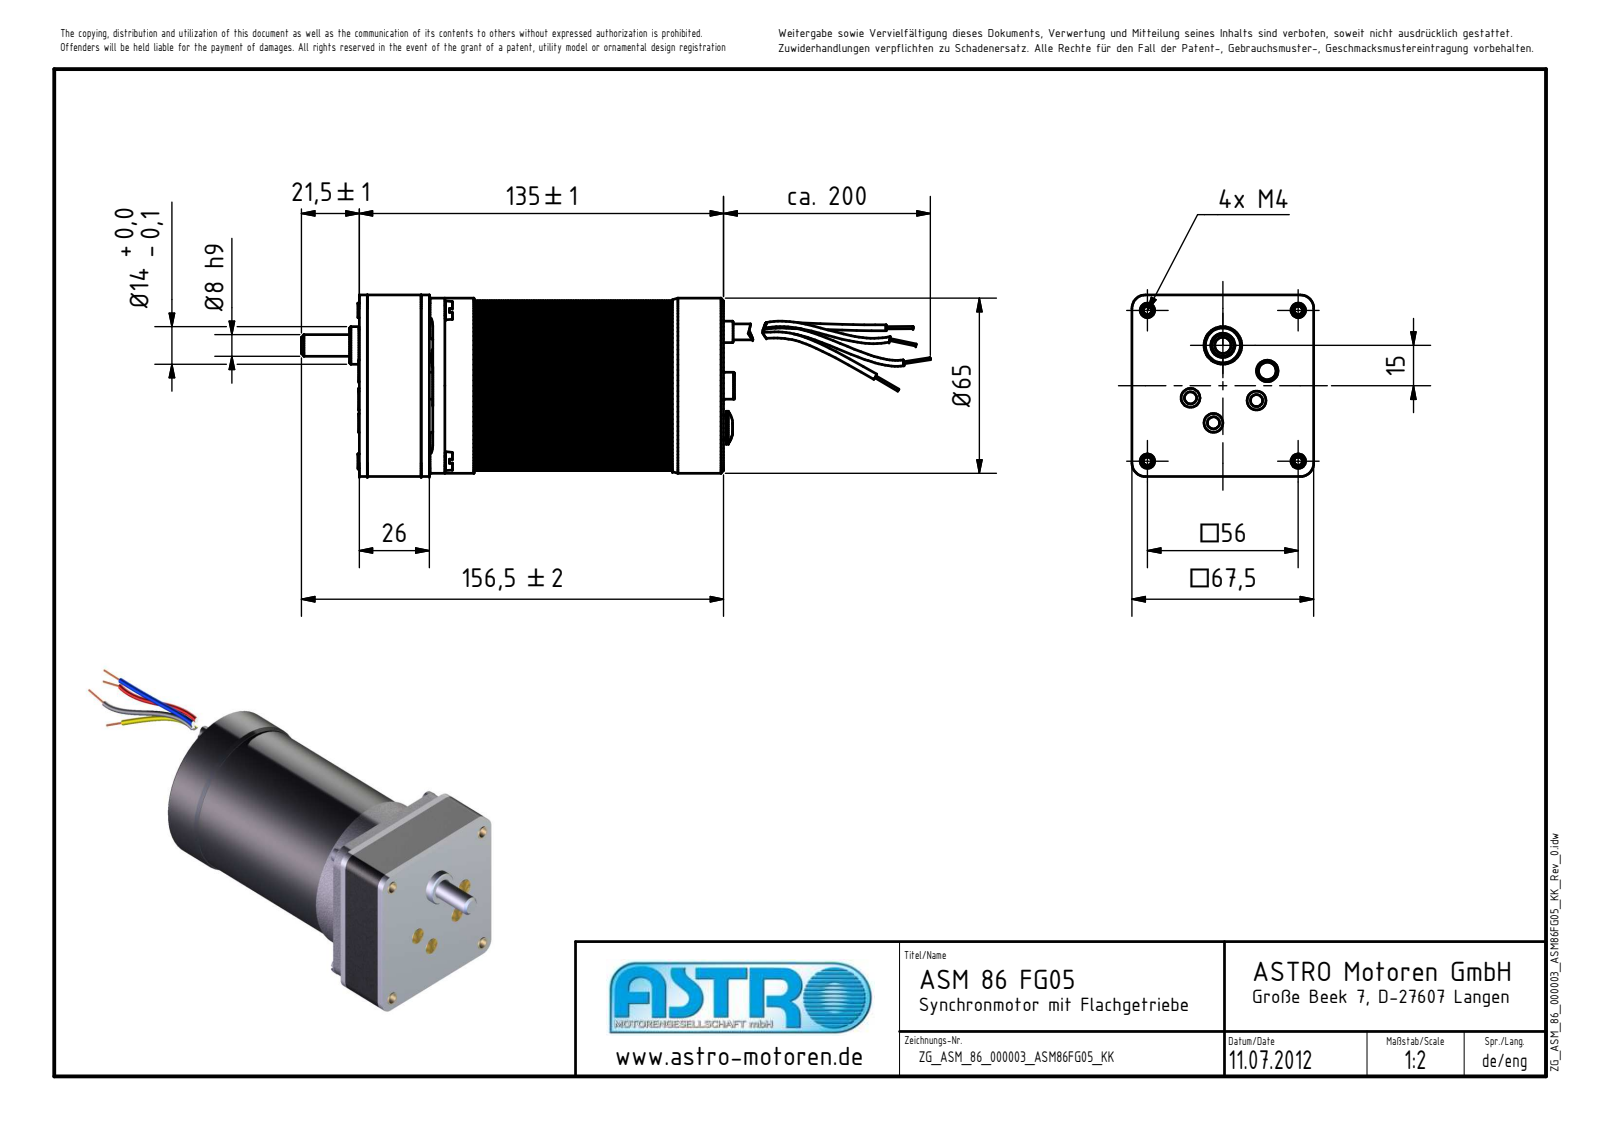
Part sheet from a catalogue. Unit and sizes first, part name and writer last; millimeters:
Units: millimetres
Overall size (bounding box): 189.4 × 67.5 × 67.5
Round holes (diameter × count): ⌀1.6 ×8, ⌀4.1 ×8, ⌀5 ×5, ⌀4.4 ×4, ⌀4.5 ×3, ⌀5.5 ×1, ⌀6 ×1, ⌀6.5 ×1, ⌀8 ×1, ⌀12 ×1, ⌀14 ×1, ⌀15.5 ×1
Round bosses / shafts (diameter × count): ⌀8 ×7, ⌀15 ×4, ⌀5.39 ×4, ⌀4.84 ×4, ⌀4 ×4, ⌀3.57 ×4, ⌀7 ×3, ⌀8.5 ×2
Partial cylindrical surfaces — rounded edges, fillets, slot ends (radius × count): R0.5 ×37, R2.25 ×8, R3.5 ×8, R3 ×4, R5 ×4, R5.26 ×4, R2 ×3, R1 ×2
Main face-to-face distances: 3, 0.65, 1.3, 1.95, 2.6, 3.25, 3.9, 23, 4.55, 5.2
Hole centre spacings: 31.46, 47, 55.42, 11.29, 27, 38.18, 54.51, 29.5
Volume: 208 150 mm³ · Surface area: 428 450 mm²
Bodies: 142 solids, 17419 faces (6321 planar, 10978 cylindrical, 120 other)
Part name (STEP PRODUCT): ZG_ASM_86_000003_ASM86FG05_KK_Rev_0; AFG-05; FG-Antriebsseite; FG-Abstandhalter (+8 more)
STEP written by: Autodesk Inventor 2010 (AUTOMOTIVE_DESIGN)
